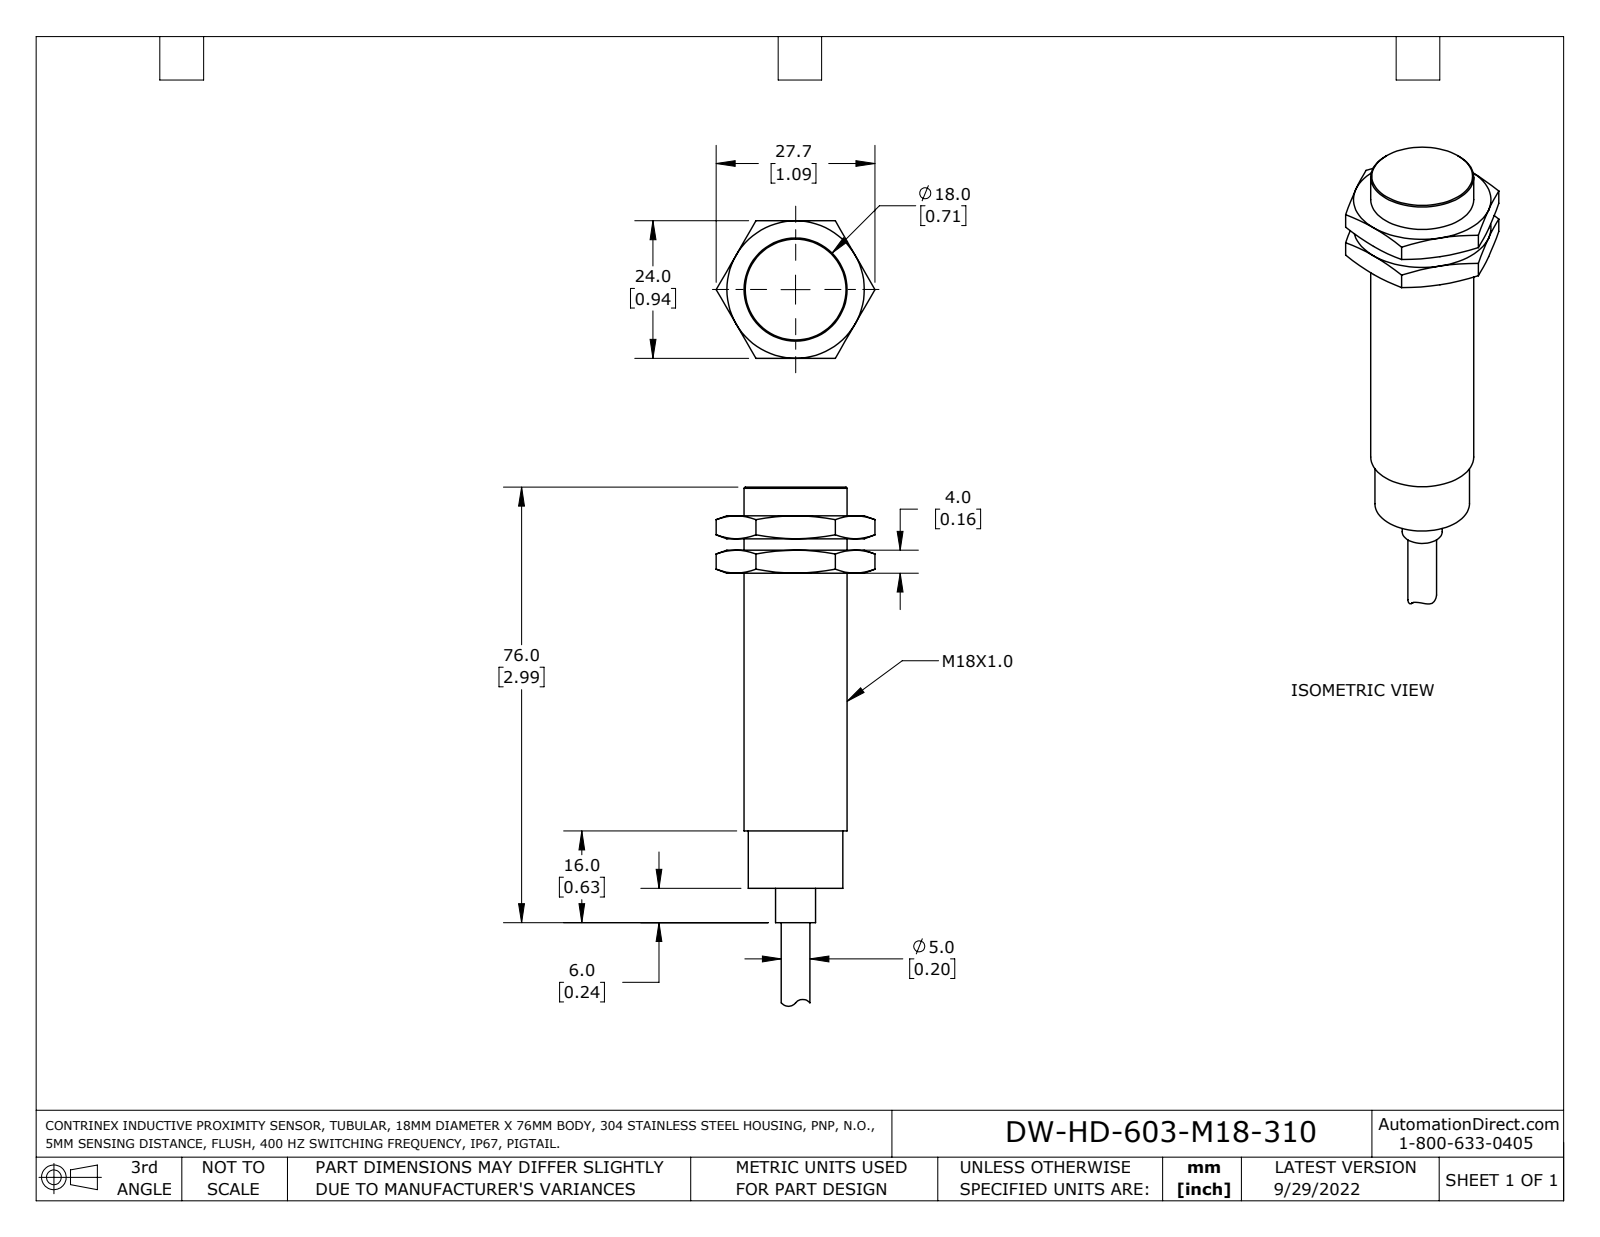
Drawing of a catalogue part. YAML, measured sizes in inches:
part_name: "DW-HD-603-M18-310"
step_written_by: "SolidWorks 2021 (AUTOMOTIVE_DESIGN)"
units: inches
bodies: {solids: 1, faces: 53, planar: 20, cylindrical: 8, other: 25}
overall_size: [3.567, 1.091, 0.945]
volume: 1.21
surface_area: 9.134
round_bosses_or_shafts:
  - {diameter: 0.709, count: 1}
  - {diameter: 0.65, count: 1}
  - {diameter: 0.276, count: 1}
  - {diameter: 0.197, count: 1}
partial_cylinders:
  - {radius: 0.063, count: 2}
face_to_face_distances: [0.236, 0.157, 0.945, 0.394, 2.165, 0.197, 0.433, 0.354, 0.079, 0.591]
